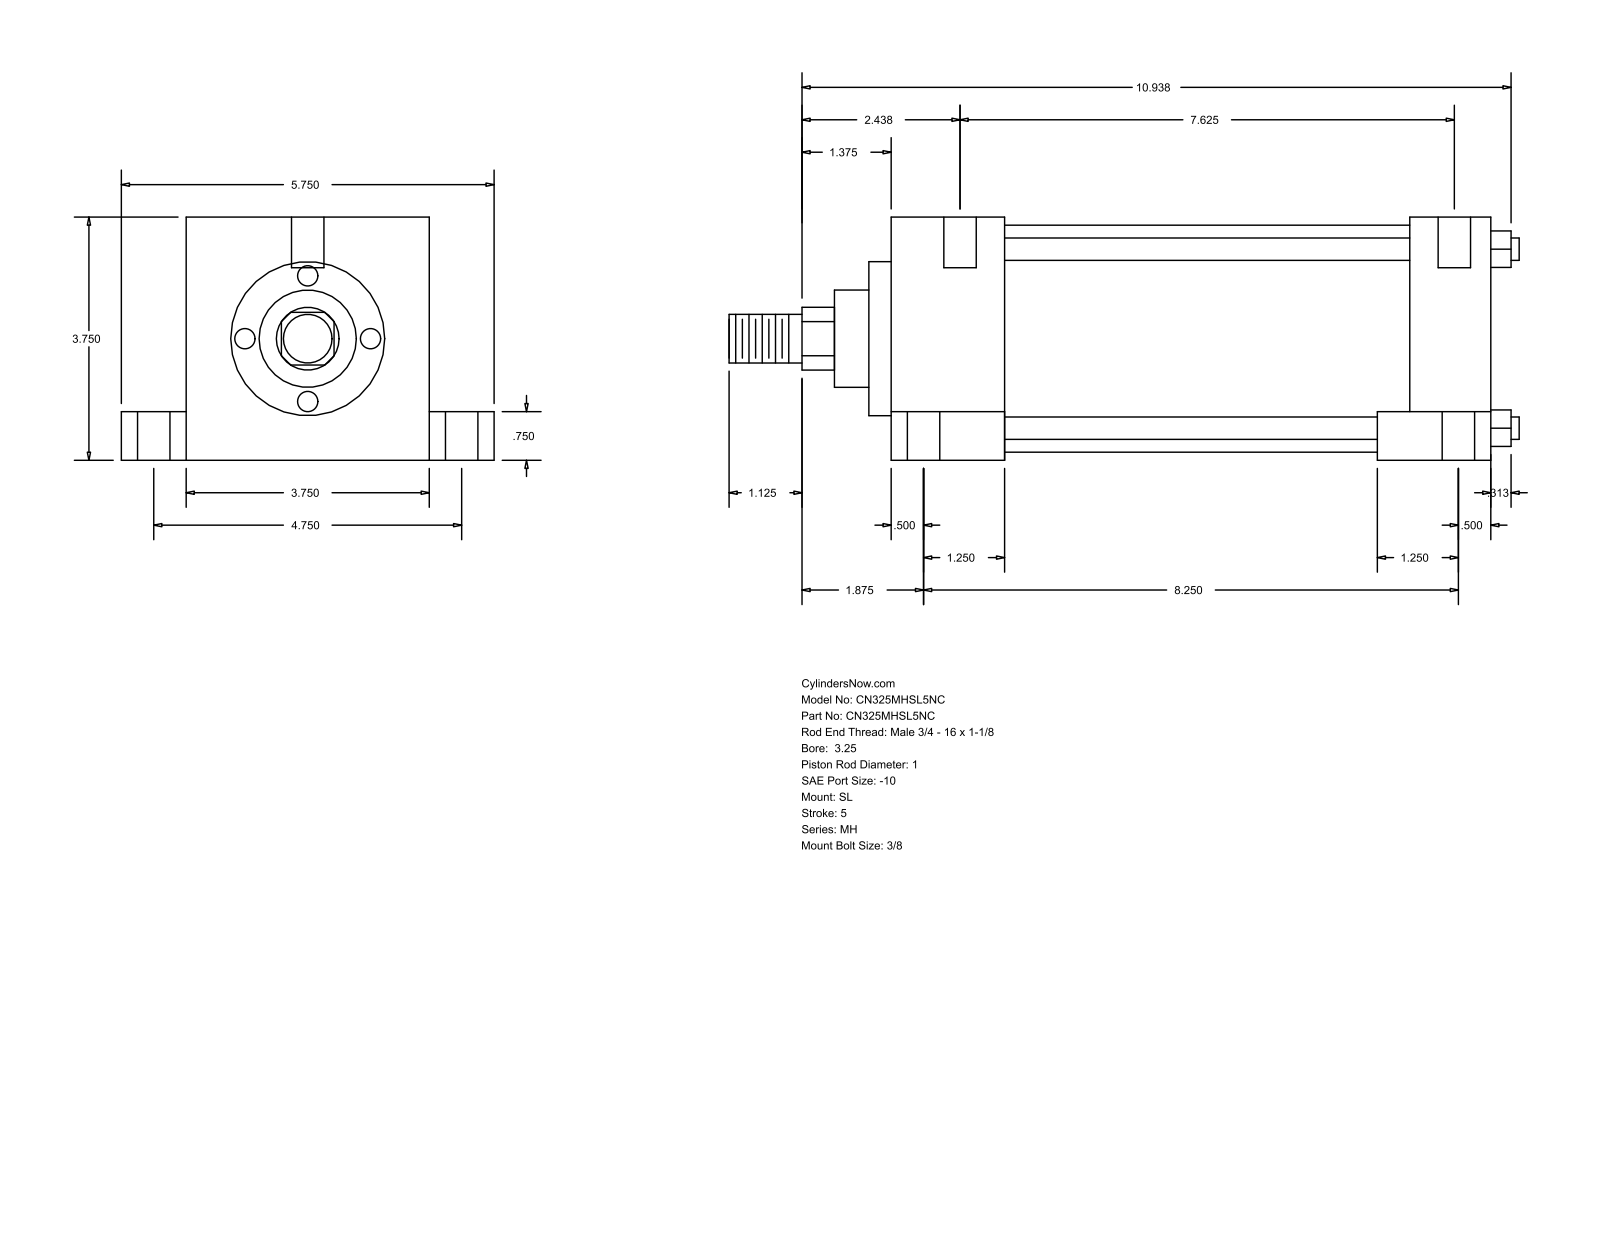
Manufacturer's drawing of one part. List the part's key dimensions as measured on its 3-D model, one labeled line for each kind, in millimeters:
Part name (STEP PRODUCT): MH_SL__0325_1
STEP written by: GSSL Pune (CONFIG_CONTROL_DESIGN)
Units: millimetres
Bodies: 0 solids, 110 faces (77 planar, 33 cylindrical, 0 other)
Overall size (bounding box): 309.56 × 146.05 × 95.25
Round holes (diameter × count): ⌀12.7 ×6, ⌀5.56 ×4, ⌀19.05 ×4
Round bosses / shafts (diameter × count): ⌀8.76 ×4, ⌀88.9 ×1, ⌀60.33 ×1, ⌀38.1 ×1, ⌀25.4 ×1, ⌀19.05 ×1
Partial cylindrical surfaces — rounded edges, fillets, slot ends (radius × count): R12.29 ×1
Main face-to-face distances: 95.24, 234.96, 44.46, 190.5, 25.41, 120.65, 19.05, 76.19, 203.2, 158.74
Hole centre spacings: 60.35, 60.41, 61.65, 62, 120.66, 200.02, 204.38, 205.89
